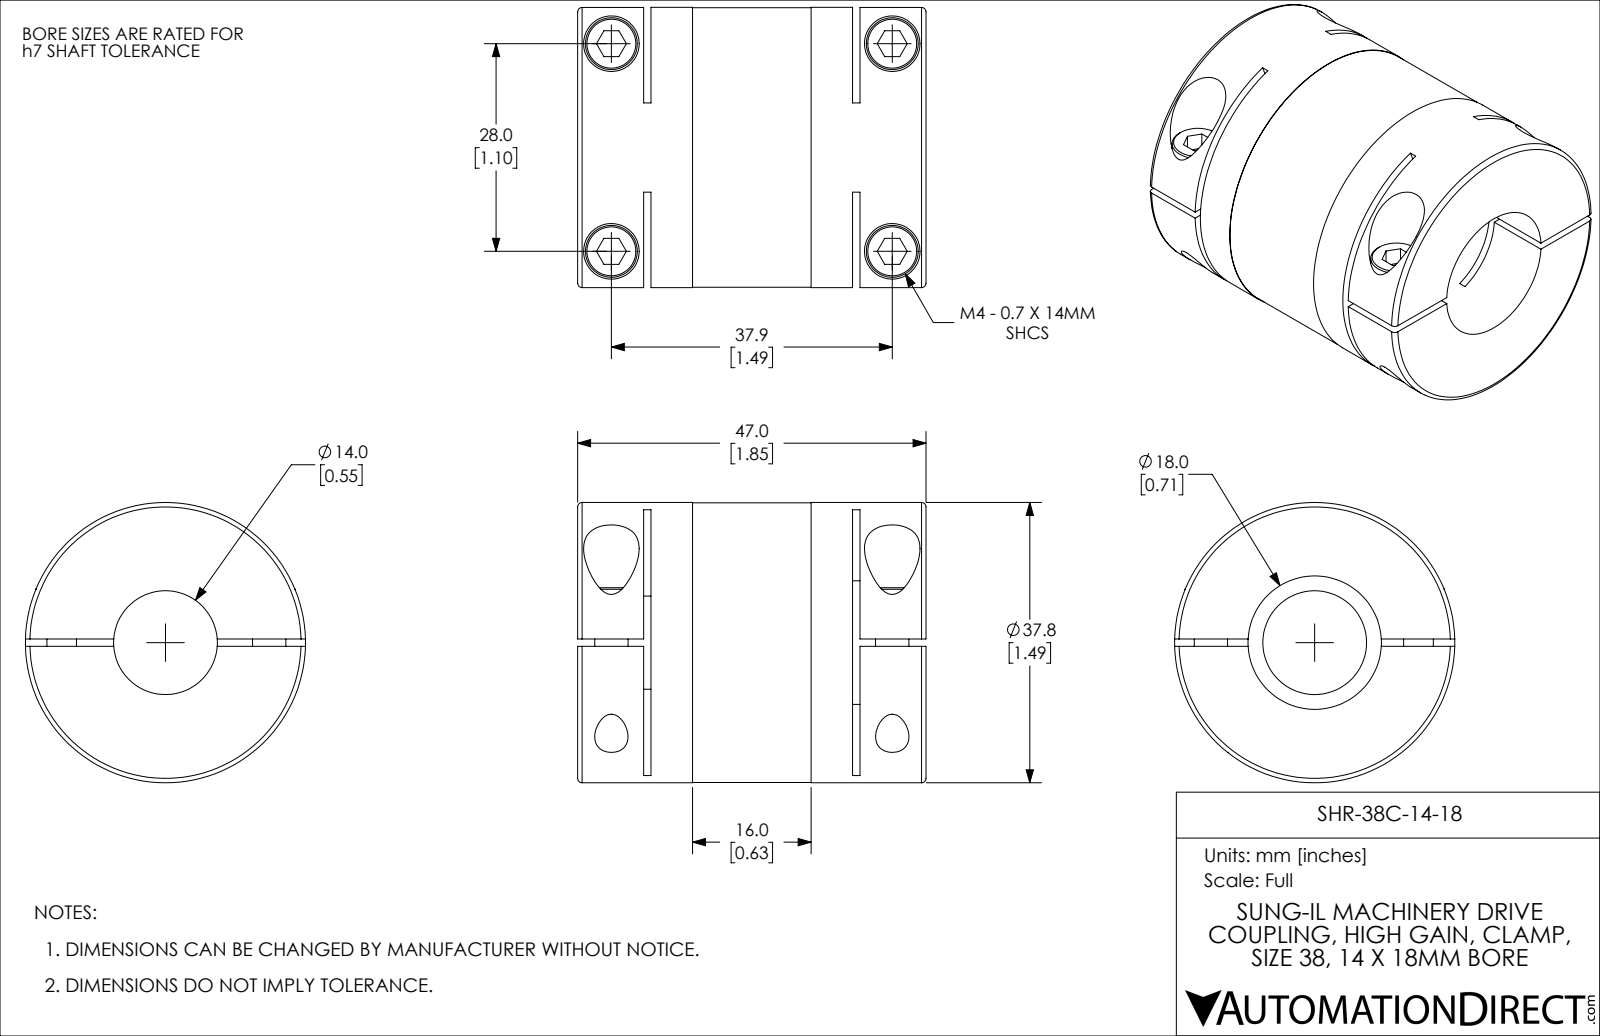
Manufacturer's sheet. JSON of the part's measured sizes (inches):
{"part_name": "SHR-38C-14-18", "step_written_by": "SolidWorks 2021 (CONFIG_CONTROL_DESIGN)", "units": "inches", "bodies": {"solids": 1, "faces": 144, "planar": 70, "cylindrical": 58, "other": 16}, "overall_size": [1.85, 1.488, 1.488], "volume_in3": 2.329, "surface_area_in2": 23.76, "round_holes": [[0.177, 4], [0.295, 4], [0.551, 1], [0.709, 1], [0.787, 1]], "round_bosses_or_shafts": [[0.276, 4], [0.157, 2], [1.488, 1], [1.484, 1]], "partial_cylinders_radius": [[1.969, 2]], "face_to_face_distances": [0.039, 0.39, 1.461, 0.35, 1.5, 1.11, 1.85, 1.071, 1.15, 1.24], "hole_center_spacings": [1.102, 1.492, 1.855]}
